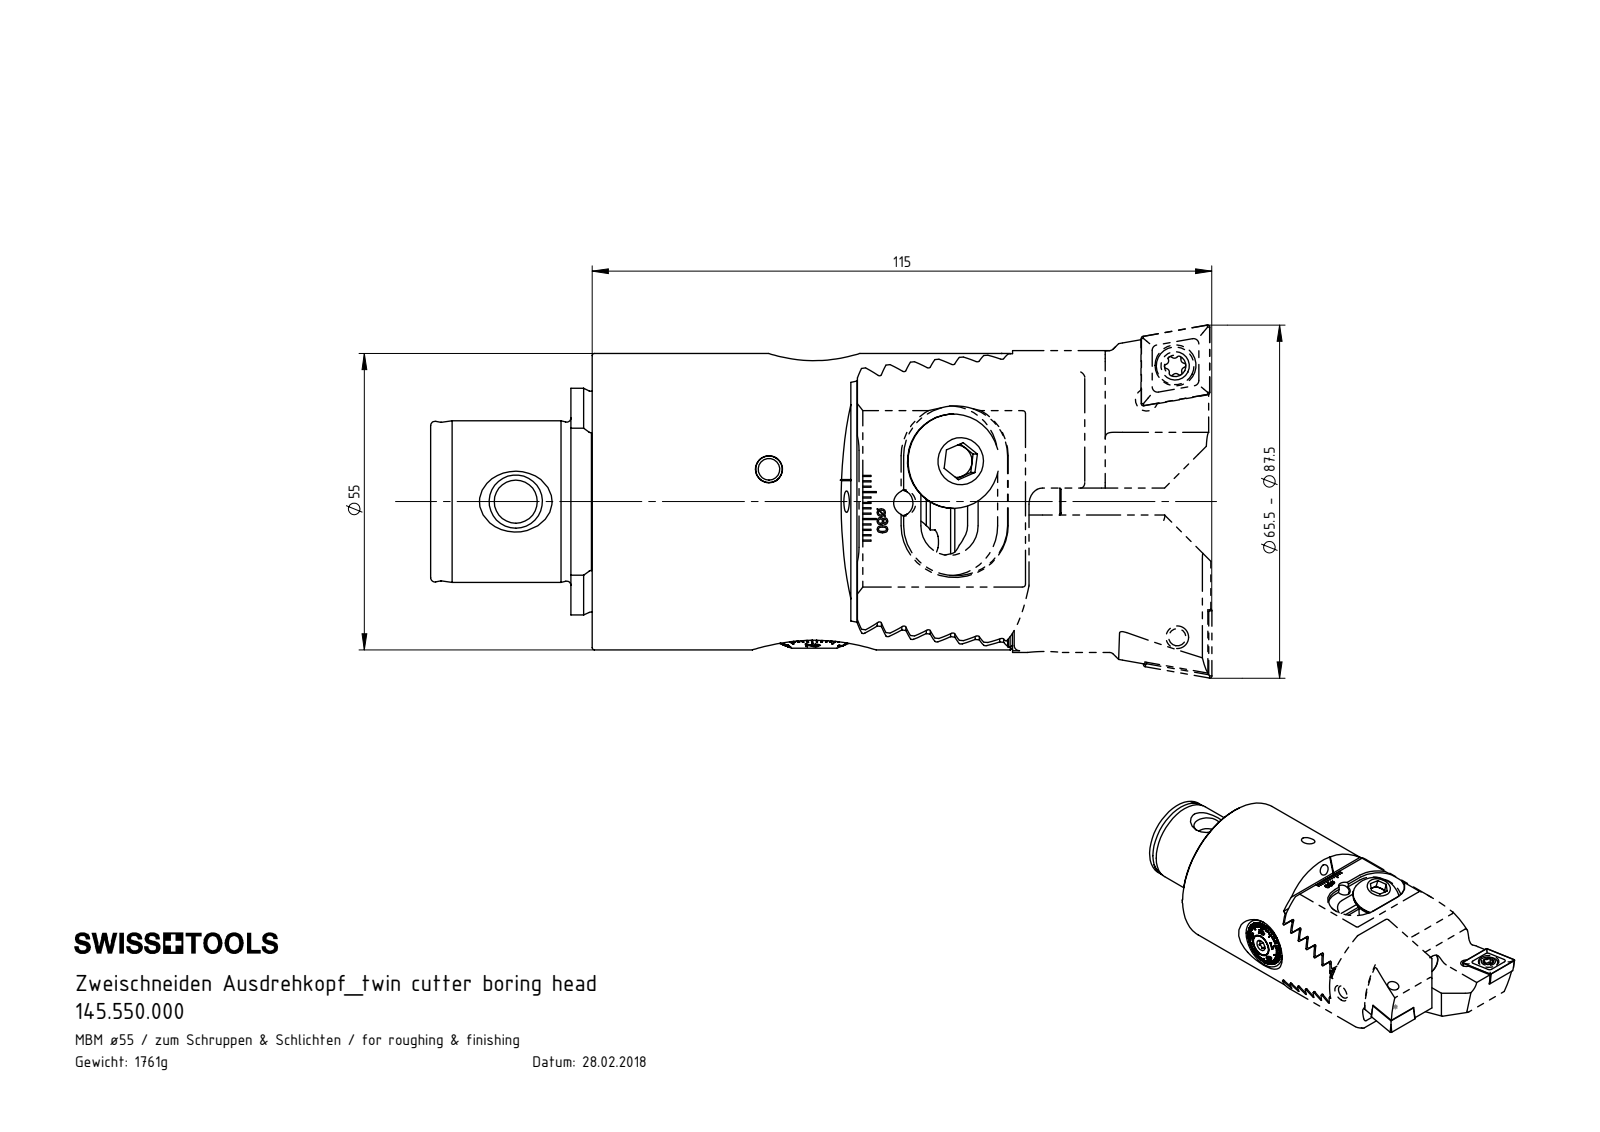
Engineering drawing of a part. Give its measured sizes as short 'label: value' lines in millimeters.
name: MB5-ZC5.K23.115_A; Z42-ER2.001.019_A; ZC5-xxx.001.037_A_versetzt Combi; WCC-ER2.001.010_A (+8 more)
written by: SolidWorks 2017 (CONFIG_CONTROL_DESIGN)
unit: mm
bodies: 22 solids, 1509 faces (738 planar, 280 cylindrical, 491 other)
size: 145 × 65.5 × 55
volume: 225 226 mm³; area: 61 642 mm²
holes: 5× ⌀5, 4× ⌀4.2, 4× ⌀8.5, 2× ⌀2, 2× ⌀3, 2× ⌀4, 2× ⌀5.5, 2× ⌀7.6, 2× ⌀8, 2× ⌀10.5, 2× ⌀11, 1× ⌀2.5
bosses: 4× ⌀5, 3× ⌀17, 3× ⌀10, 2× ⌀17.5, 2× ⌀7, 2× ⌀4, 1× ⌀55, 1× ⌀30
rounds: 14× R0.34, 14× R1, 12× R0.34, 12× R0.39, 8× R0.69, 4× R0.69, 4× R3, 4× R5.5
face distances: 4.07, 8.14, 12.21, 16.28, 4.11, 20.35, 4.03, 8.18, 4.01, 7.85
hole spacings: 44.41, 44.51, 50.43, 8.08, 8.2, 8.21, 8.33, 8.75
